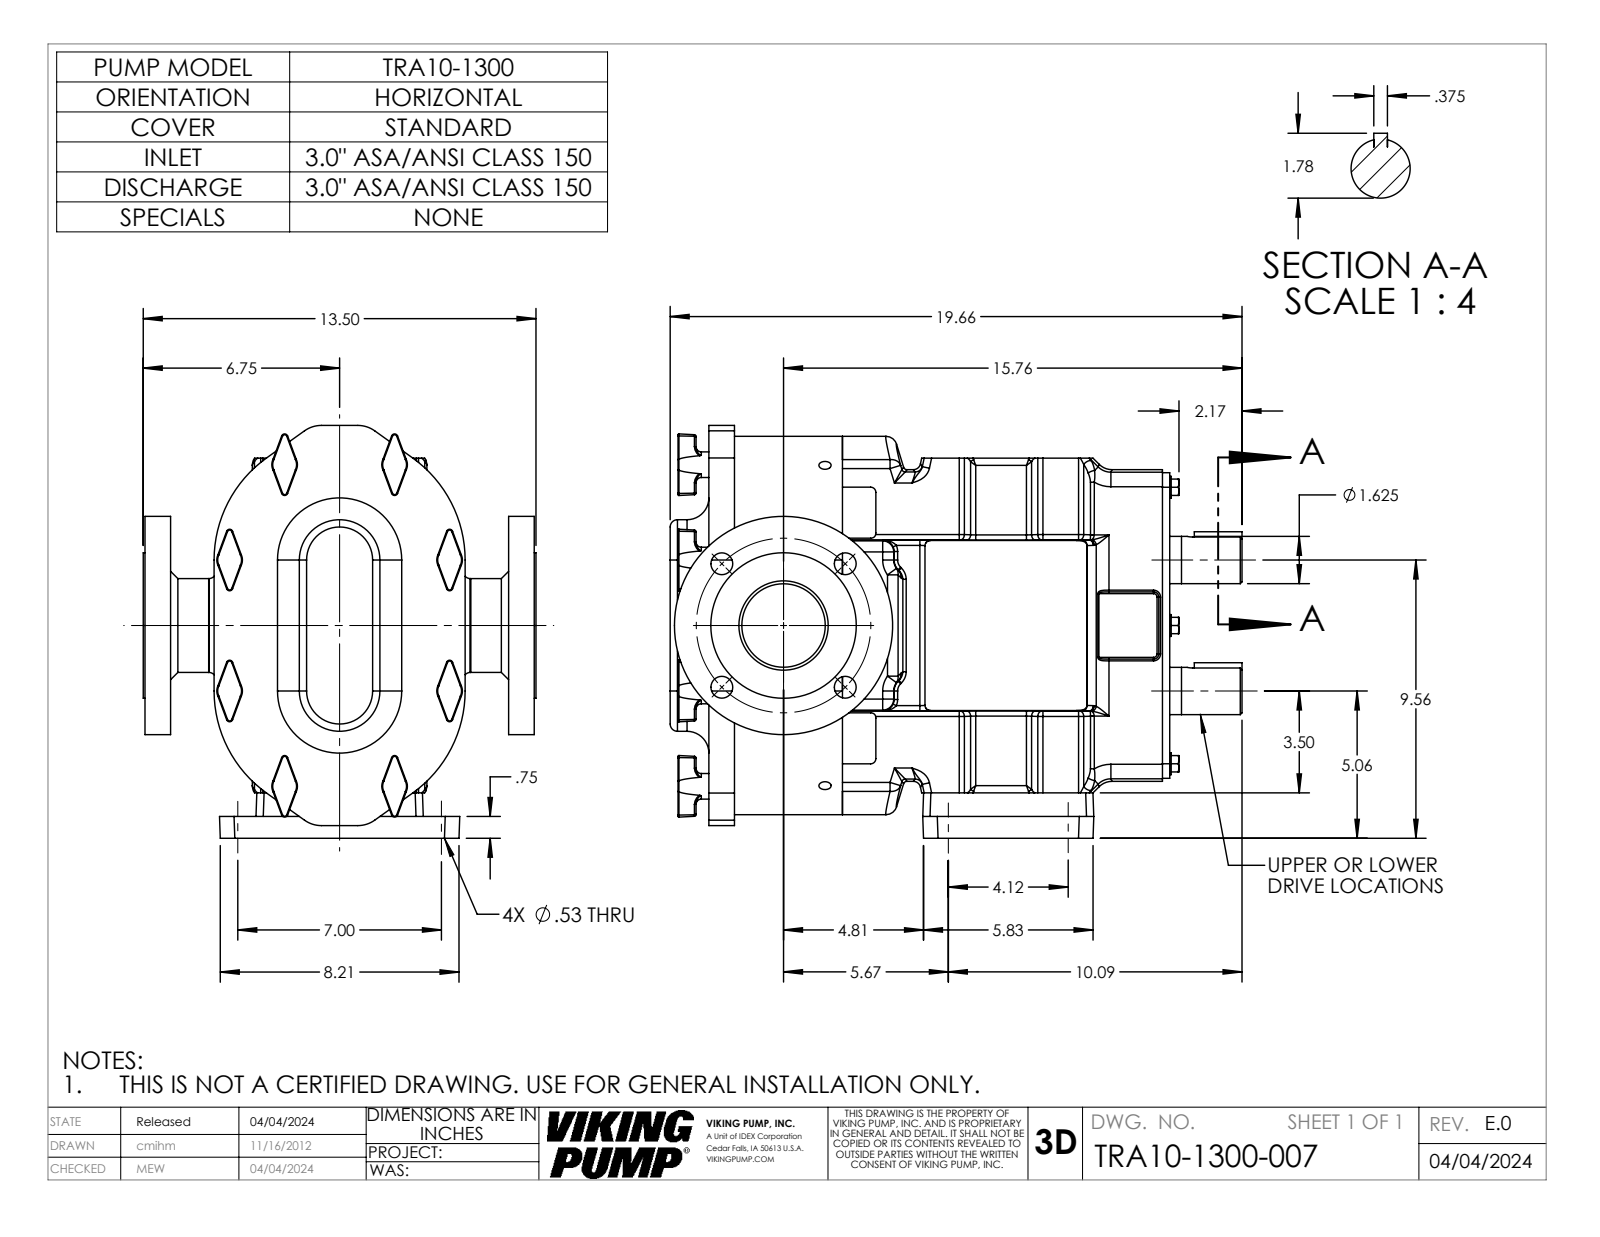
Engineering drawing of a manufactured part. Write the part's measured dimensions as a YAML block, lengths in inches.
part_name: "TRA10-1300-007; 1300FLG150-30; TRA10-0600-GEARBOX-H; TRA10-0600-COVER-STD (+1 more)"
step_written_by: "SolidWorks 2022 (AUTOMOTIVE_DESIGN)"
units: inches
bodies: {solids: 5, faces: 1089, planar: 289, cylindrical: 404, other: 396}
overall_size: [19.656, 14.185, 13.5]
volume: 1341
surface_area: 1603
round_holes:
  - {diameter: 0.332, count: 4}
  - {diameter: 0.531, count: 4}
  - {diameter: 0.75, count: 4}
  - {diameter: 2.868, count: 1}
  - {diameter: 3.07, count: 1}
round_bosses_or_shafts:
  - {diameter: 0.88, count: 8}
  - {diameter: 0.75, count: 6}
  - {diameter: 1.624, count: 2}
  - {diameter: 7.5, count: 1}
  - {diameter: 5, count: 1}
  - {diameter: 3.224, count: 1}
partial_cylinders:
  - {radius: 0.18, count: 44}
  - {radius: 0.06, count: 43}
  - {radius: 0.03, count: 32}
  - {radius: 0.25, count: 32}
  - {radius: 0.38, count: 28}
  - {radius: 0.12, count: 24}
  - {radius: 0.5, count: 20}
  - {radius: 0.375, count: 12}
face_to_face_distances: [3.712, 0.88, 0.5, 2.31, 9.31, 11.25, 4.592, 15.842, 14.962, 2.81]
hole_center_spacings: [3, 2.895, 4.12, 4.243, 4.243, 6, 7, 8.122]
